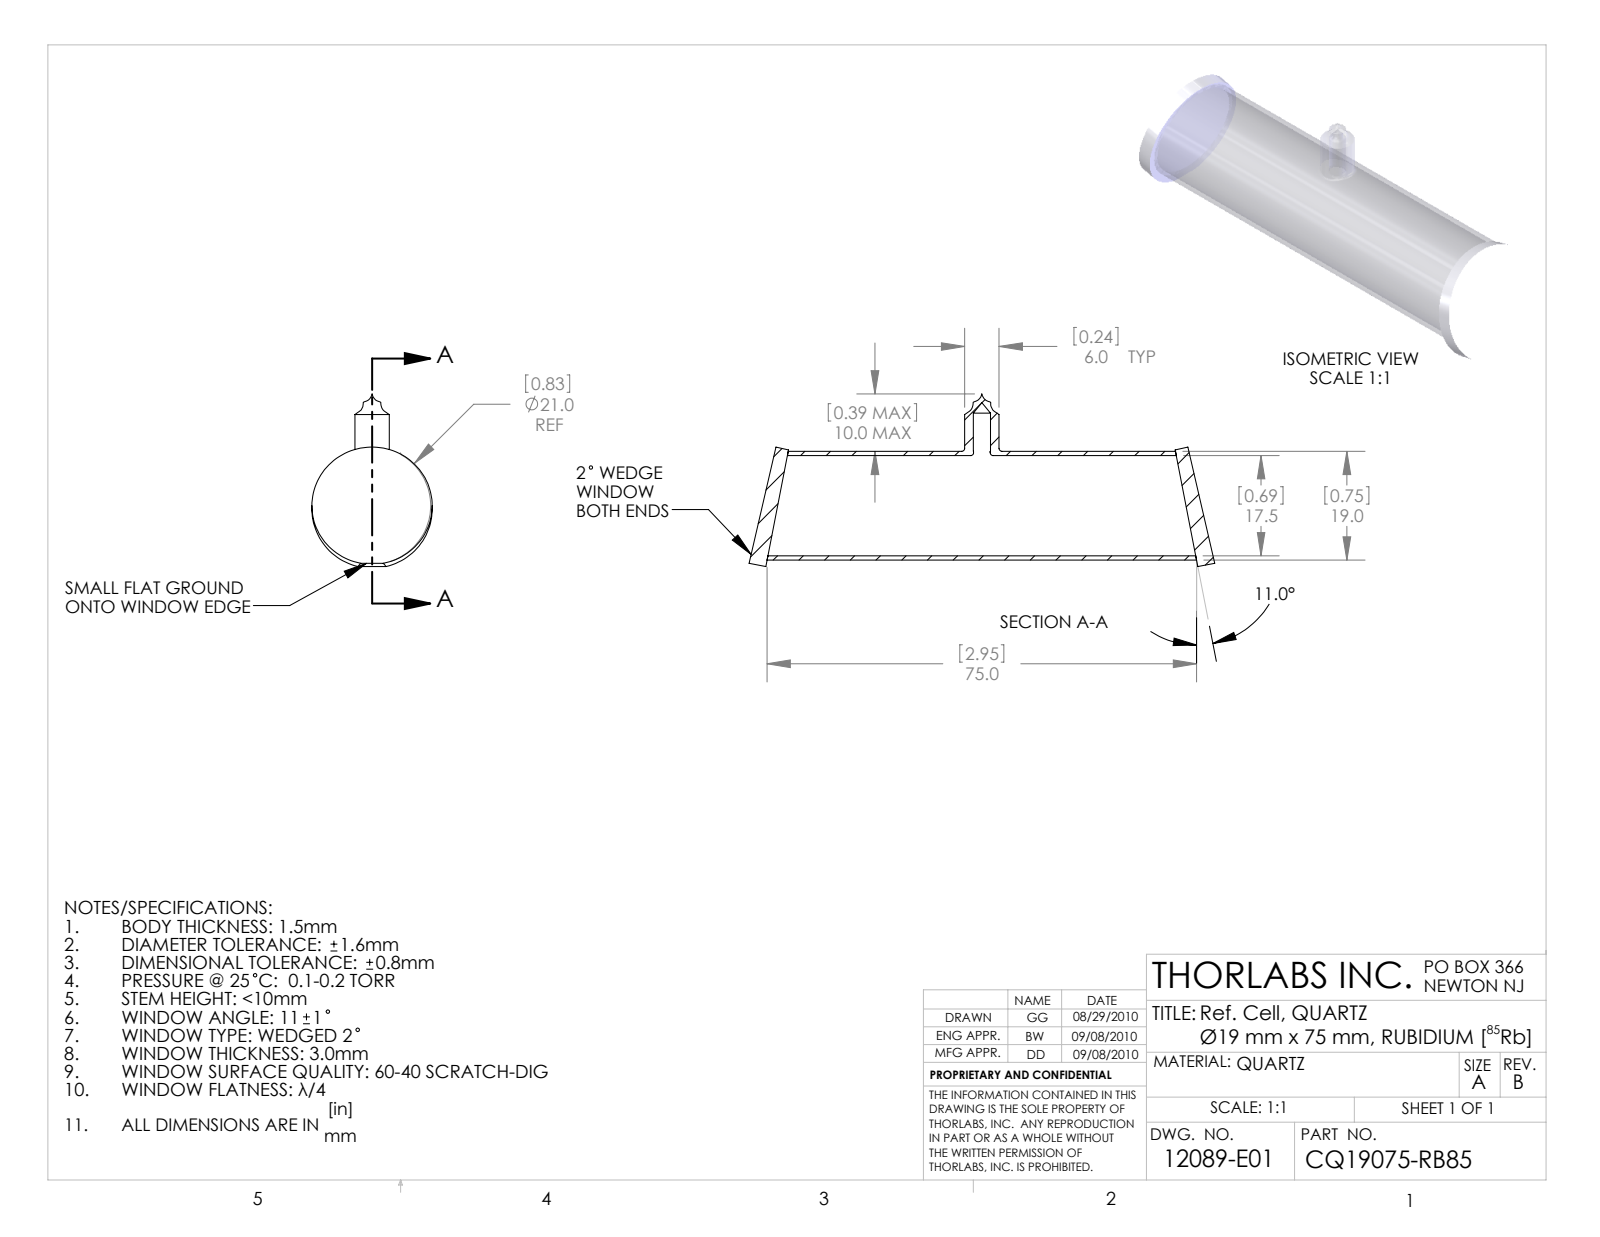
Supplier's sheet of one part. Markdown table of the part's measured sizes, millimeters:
| quantity | value |
| --- | --- |
| part name | 12089-E0W |
| STEP written by | SolidWorks 2009 (AUTOMOTIVE_DESIGN) |
| units | millimeters |
| bodies | 3 solids, 33 faces (8 planar, 17 cylindrical, 8 other) |
| overall size | 81.31 × 30.12 × 21 |
| volume | 5 042 mm³ |
| surface area | 10 206 mm² |
| round holes (diameter × count) | 2.91 × 1, 3 × 1, 17.5 × 1 |
| round bosses / shafts (diameter × count) | 21 × 2, 19 × 1, 6 × 1 |
